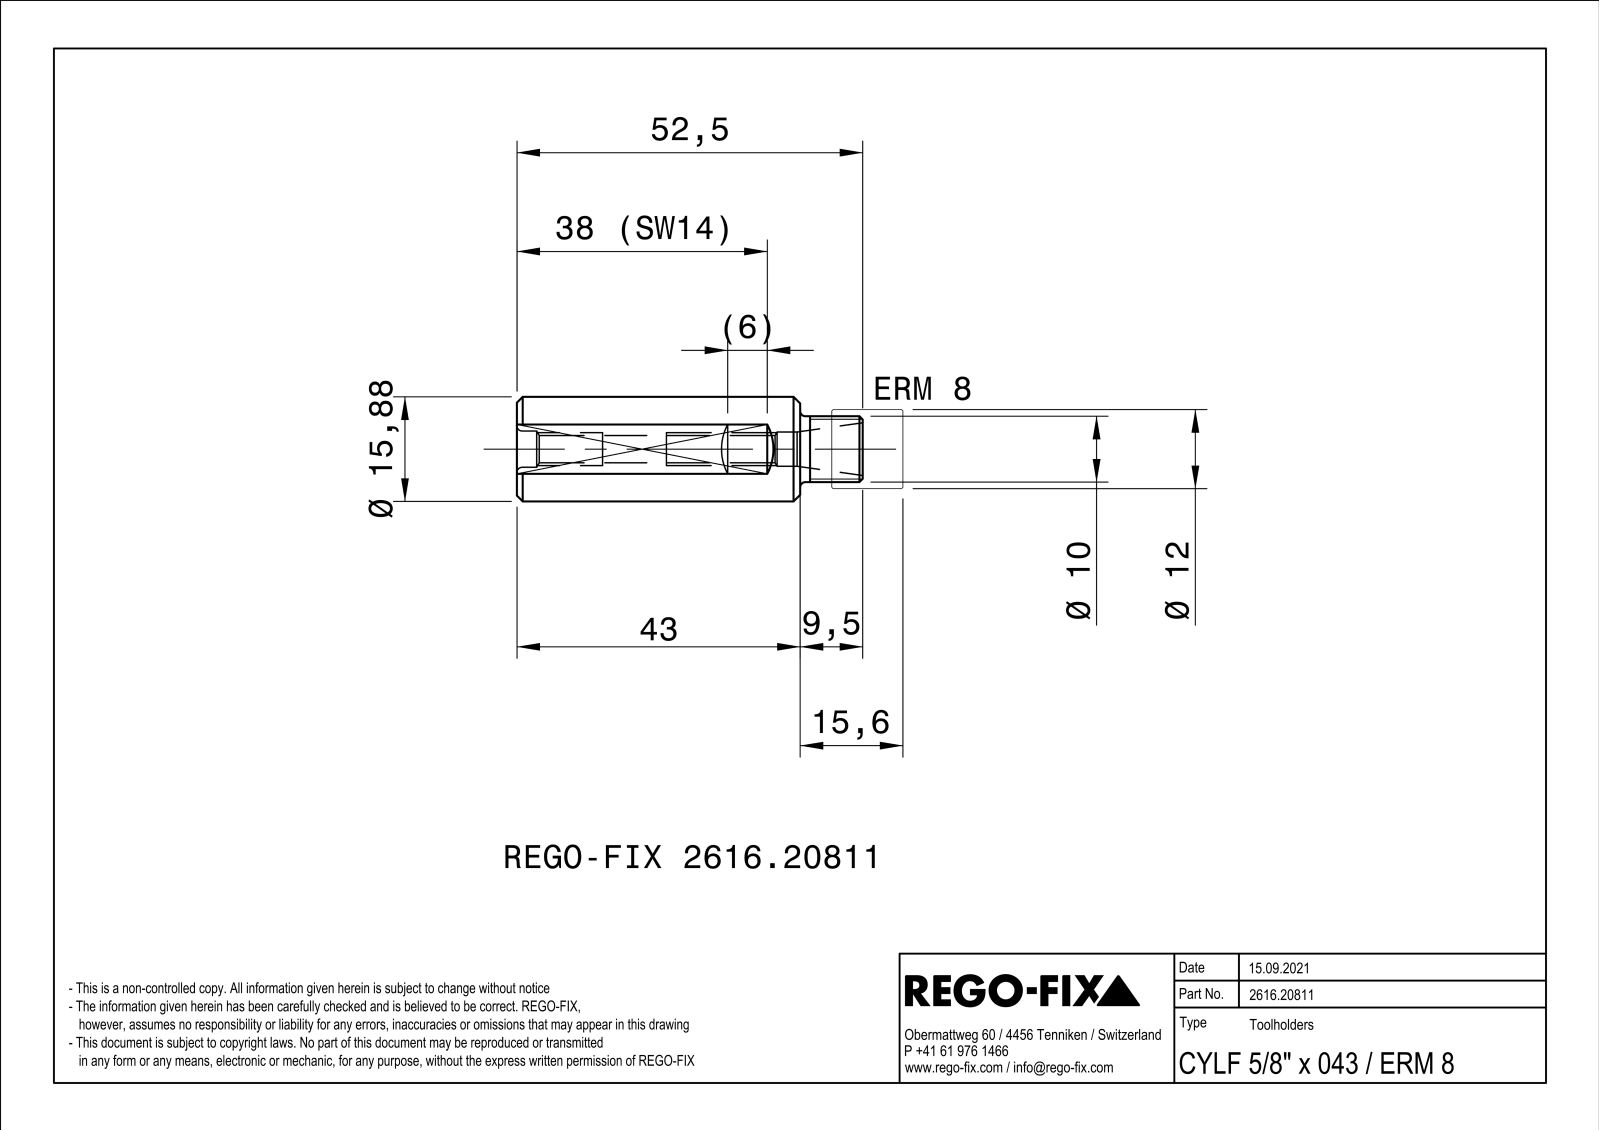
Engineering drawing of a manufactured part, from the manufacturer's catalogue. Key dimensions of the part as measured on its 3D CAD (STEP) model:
Part name (STEP PRODUCT): NOCUT
STEP written by: SIEMENS PLM Software Solid Edge ST10 (AUTOMOTIVE_DESIGN)
Units: millimetres
Bodies: 1 solid, 26 faces (9 planar, 8 cylindrical, 9 other)
Overall size (bounding box): 52.5 × 15.88 × 15.88
Volume: 8 024 mm³ · Surface area: 3 463 mm²
Round holes (diameter × count): ⌀4.13 ×1, ⌀5.2 ×1, ⌀5.5 ×1
Round bosses / shafts (diameter × count): ⌀15.87 ×1, ⌀10 ×1
Main face-to-face distances: 43, 14, 9.5, 52.5, 26.27, 5.65, 31.92
